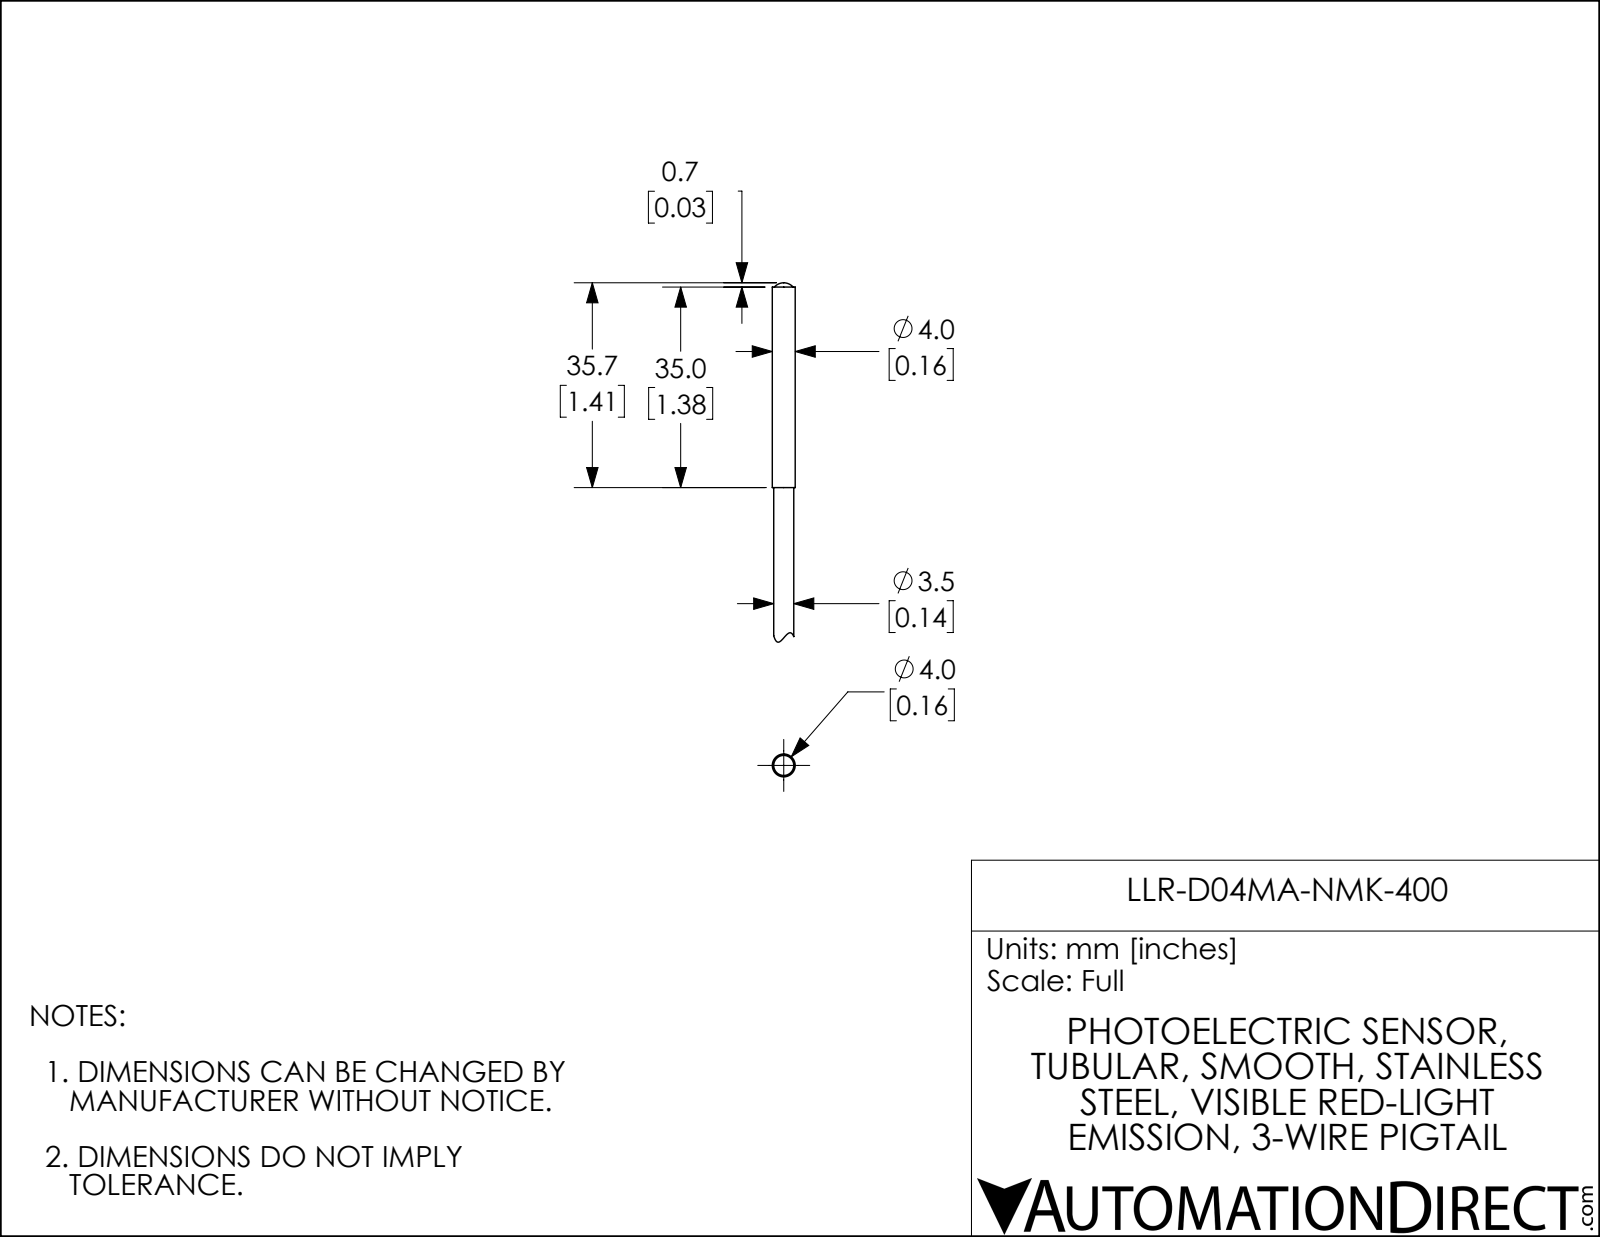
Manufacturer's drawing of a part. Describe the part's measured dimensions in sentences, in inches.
The part is named "LLR-D04MA-Nxx-400". Its 3-D file was written by "SolidWorks 2018 (AUTOMOTIVE_DESIGN)". It is 1 solid with 6 faces: 2 planar, 2 cylindrical and 2 other. Overall it measures 2.47 by 0.157 by 0.157 inches. Its volume is 0.042 cubic inches and its surface area 1.174 square inches. Round bosses or shafts: 1 of diameter 0.157, 1 of diameter 0.138. The main face-to-face distances are 1.378.
